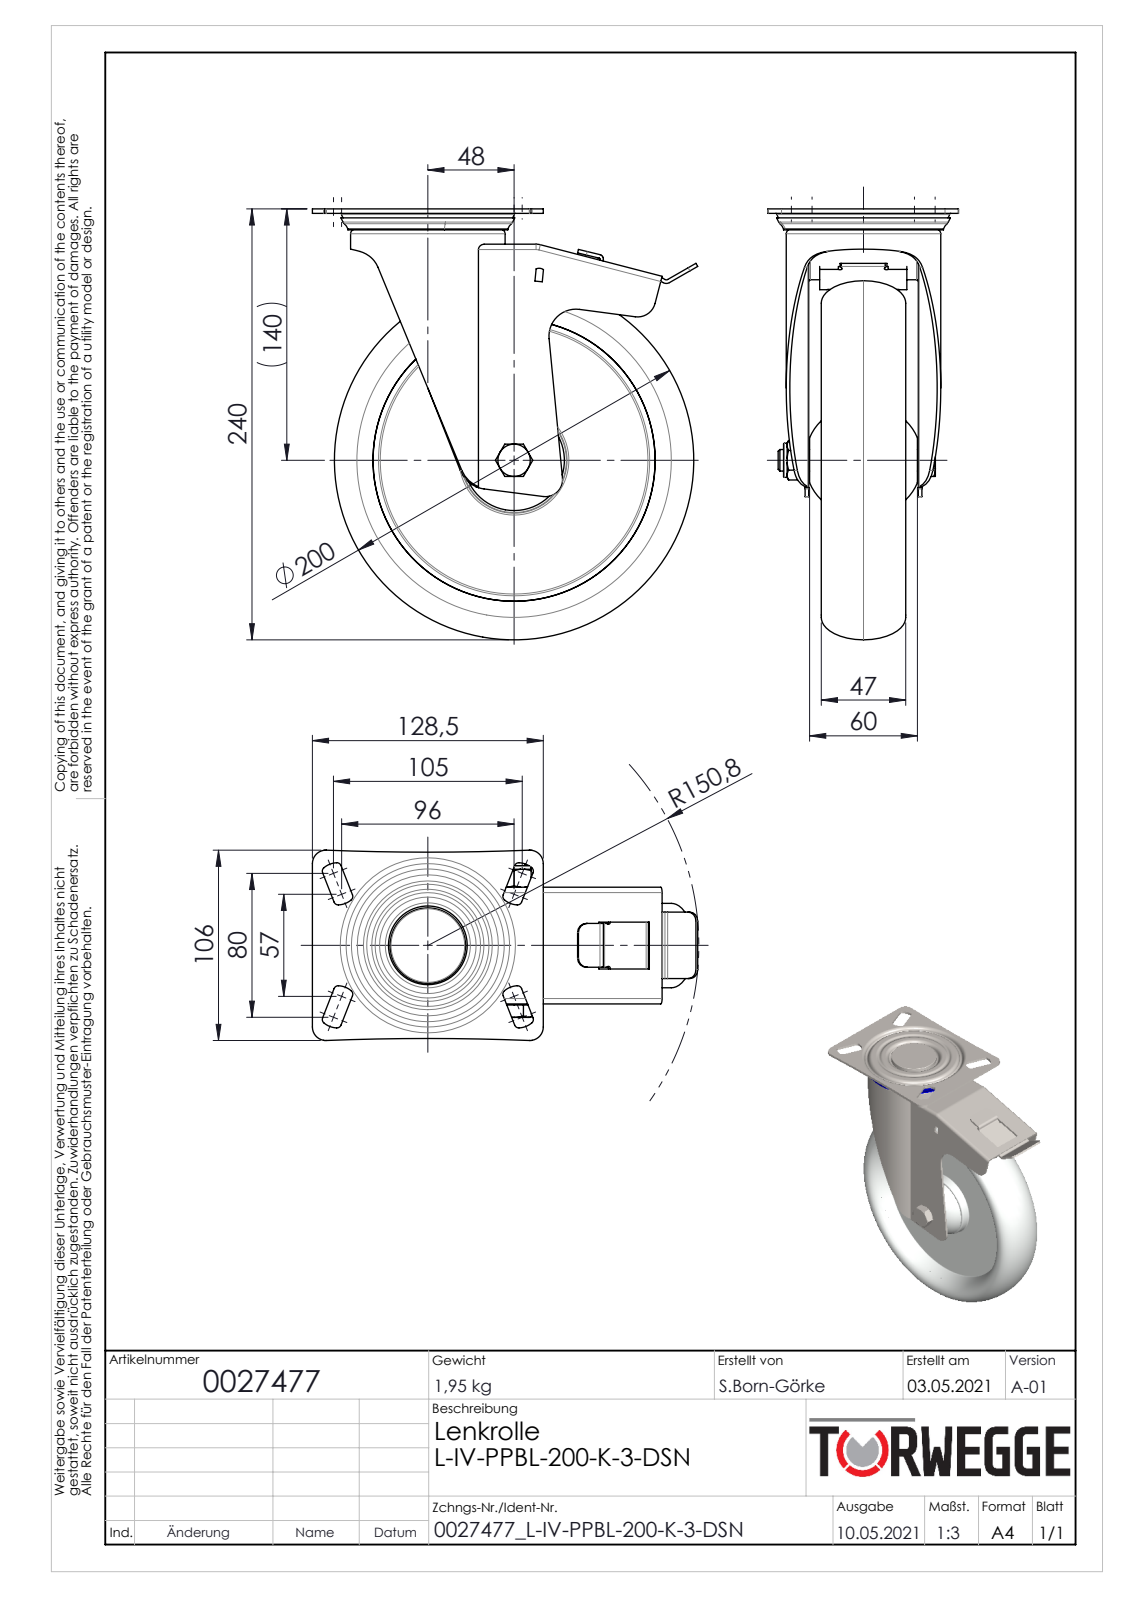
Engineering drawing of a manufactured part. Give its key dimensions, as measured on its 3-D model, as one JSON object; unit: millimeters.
{"part_name": "0027477", "step_written_by": "SolidWorks 2020 (AUTOMOTIVE_DESIGN)", "units": "millimeters", "bodies": {"solids": 11, "faces": 513, "planar": 133, "cylindrical": 133, "other": 247}, "overall_size": [240, 214.44, 106], "volume_mm3": 905877, "surface_area_mm2": 312460, "round_holes": [[10.2, 1], [12, 1], [12.3, 1], [34, 1], [38, 1], [44, 1], [47, 1], [50.5, 1], [54, 1], [82, 1]], "round_bosses_or_shafts": [[89, 1], [86, 1], [54.5, 1], [42, 1], [41, 1], [38, 1], [20, 1], [19, 1]], "partial_cylinders_radius": [[2.5, 17], [1.25, 5], [7.5, 5], [1, 4], [3, 4], [11.75, 4], [1.5, 2], [2, 2]], "face_to_face_distances": [2, 27, 38, 11, 63, 25, 36, 2.5, 65, 61]}
